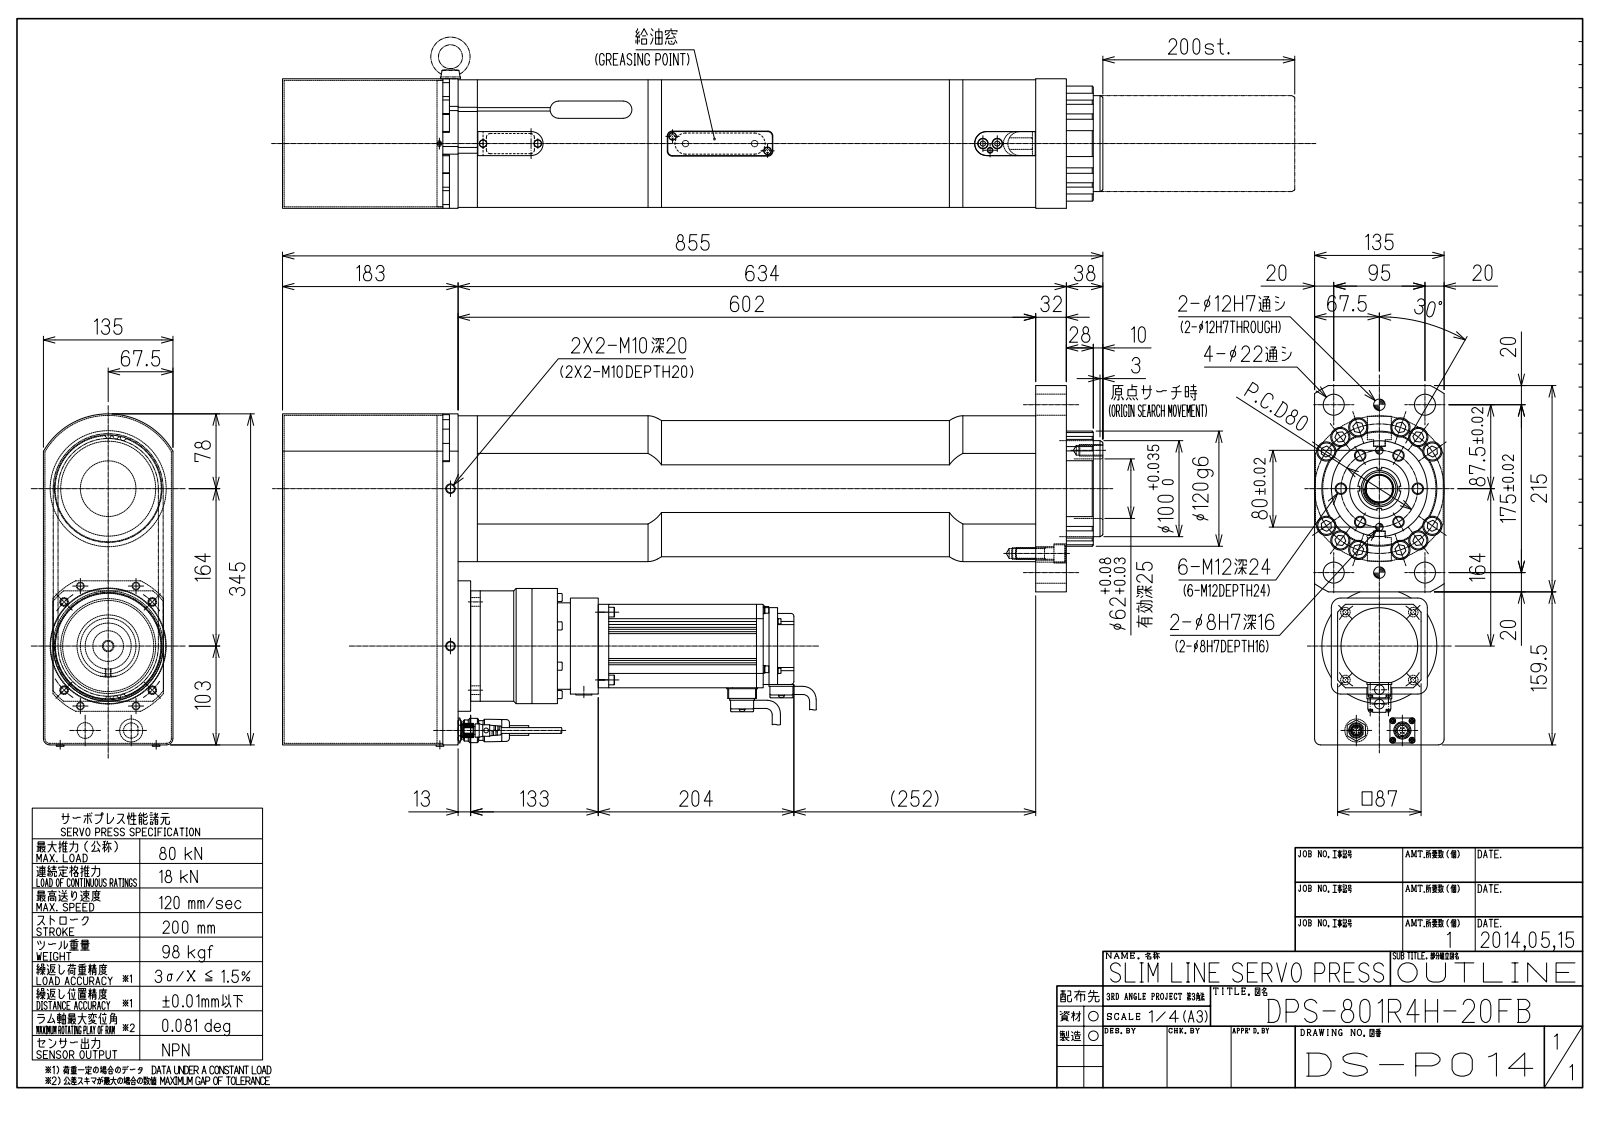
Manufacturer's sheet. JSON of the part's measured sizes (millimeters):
{"part_name": "DPS-801R4H-20FB_OUTLINE; DS-P001-02+A_U; DPS-801R4H-20FB(DS-P014)_OUTLINE", "step_written_by": "Autodesk Inventor 2015 (AUTOMOTIVE_DESIGN)", "units": "millimeters", "bodies": {"solids": 3, "faces": 1071, "planar": 579, "cylindrical": 369, "other": 123}, "overall_size": [855, 374.5, 135], "volume_mm3": 22010000, "surface_area_mm2": 1181000, "round_holes": [[4.92, 8], [6.65, 8], [3.24, 7], [10.11, 6], [4.5, 4], [6.5, 4], [8, 4], [9, 4], [22, 4], [2.46, 2], [6.6, 2], [8.38, 2]], "round_bosses_or_shafts": [[18, 7], [8.8, 4], [7.5, 4], [7, 4], [142, 1], [120, 1], [119.7, 1], [114.7, 1]], "partial_cylinders_radius": [[1, 50], [2, 35], [5, 17], [0.5, 12], [10, 11], [3, 9], [4, 9], [2.5, 6]], "face_to_face_distances": [135, 817, 10, 78.5, 111, 6.5, 13, 634, 183, 72], "hole_center_spacings": [40, 82.01, 47.5, 69.28, 10.26, 14.99, 20.71, 23.69]}
